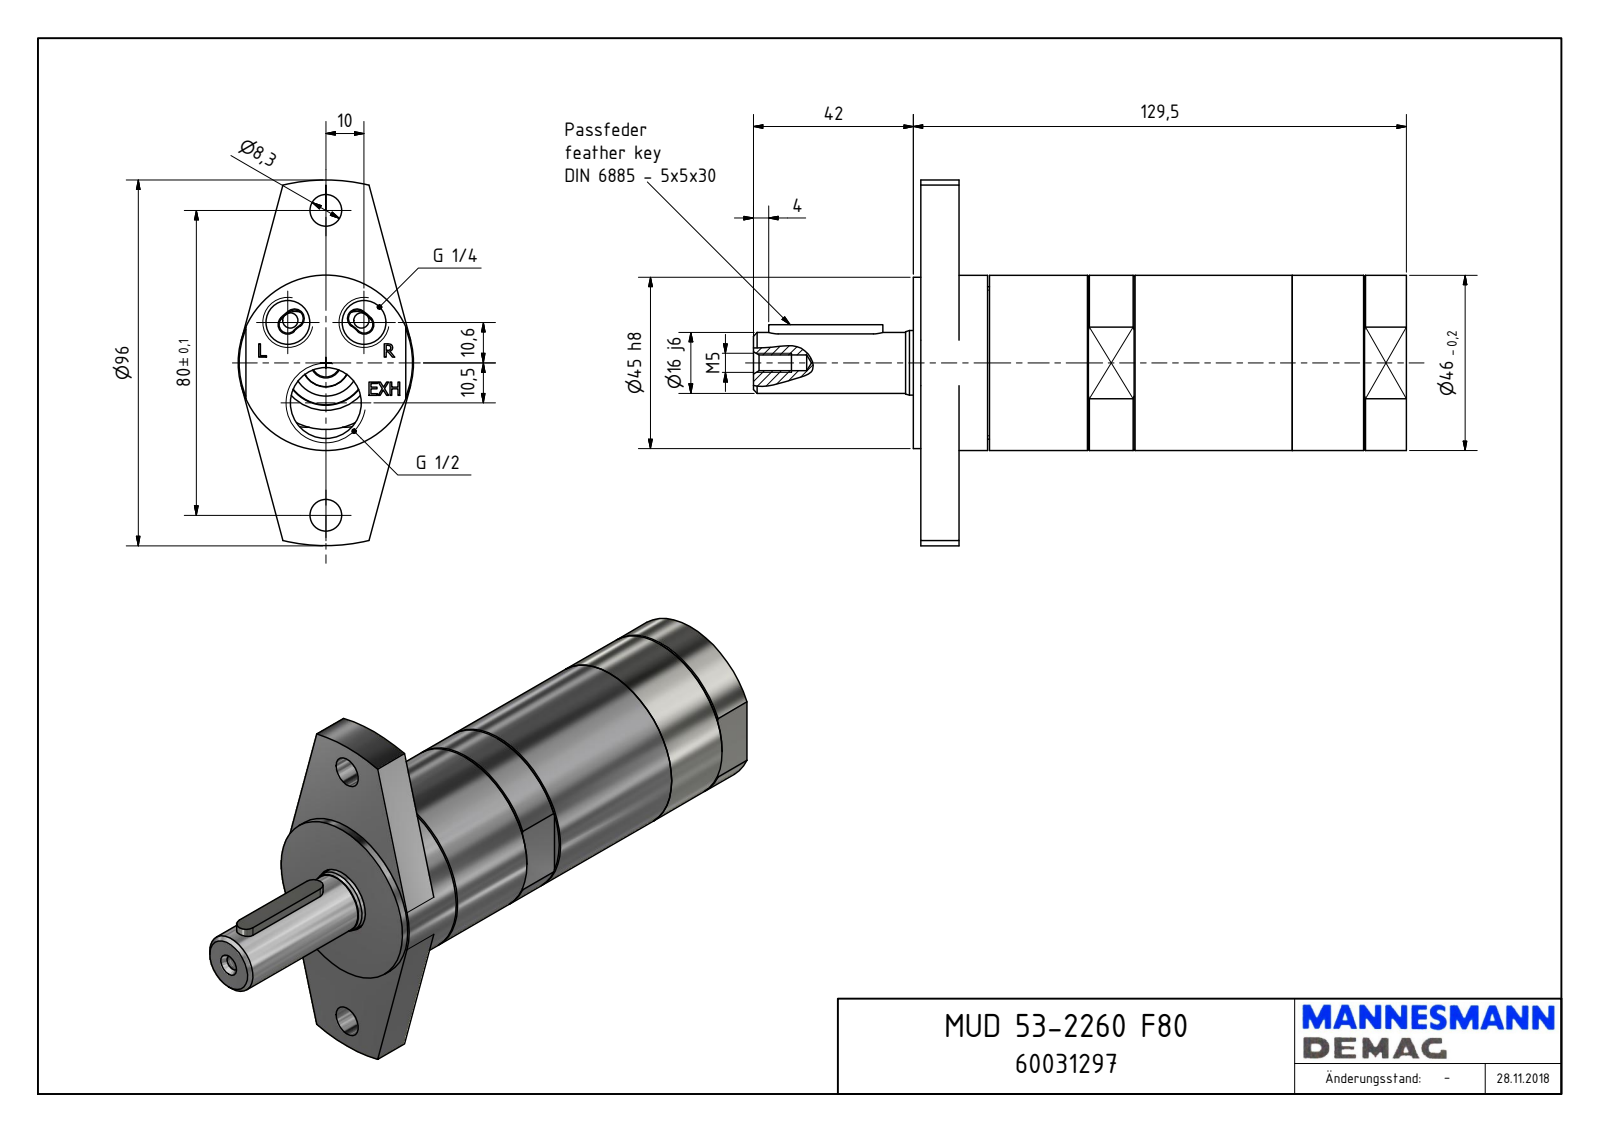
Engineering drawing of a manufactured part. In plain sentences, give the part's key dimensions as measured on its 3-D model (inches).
The part is named "MUD 53-2260 F80_60031297". Its 3-D file was written by "Autodesk Inventor 2018 (AUTOMOTIVE_DESIGN)". It is 1 solid with 164 faces: 95 planar, 30 cylindrical and 39 other. Overall it measures 6.752 by 3.78 by 1.811 inches. Its volume is 14.23 cubic inches and its surface area 51.17 square inches. Round holes: 2 of diameter 0.327, 2 of diameter 0.451, 1 of diameter 0.163, 1 of diameter 0.689, 1 of diameter 0.733, 1 of diameter 0.846, 1 of diameter 0.906. Round bosses or shafts: 1 of diameter 1.811, 1 of diameter 1.772, 1 of diameter 0.77, 1 of diameter 0.667, 1 of diameter 0.63. Partial cylindrical surfaces (rounded edges, fillets, slot ends): 2 of radius 0.098, 2 of radius 0.197, 1 of radius 0.748, 1 of radius 1.89. The main face-to-face distances are 0.394, 0.472, 0.079, 5.098, 5.02, 4.626, 1.654, 1.811, 1.812, 0.315. The hole center spacings are 0.574, 0.919, 1.222, 1.575, 2.031, 0.413, 0.787, 1.161.
